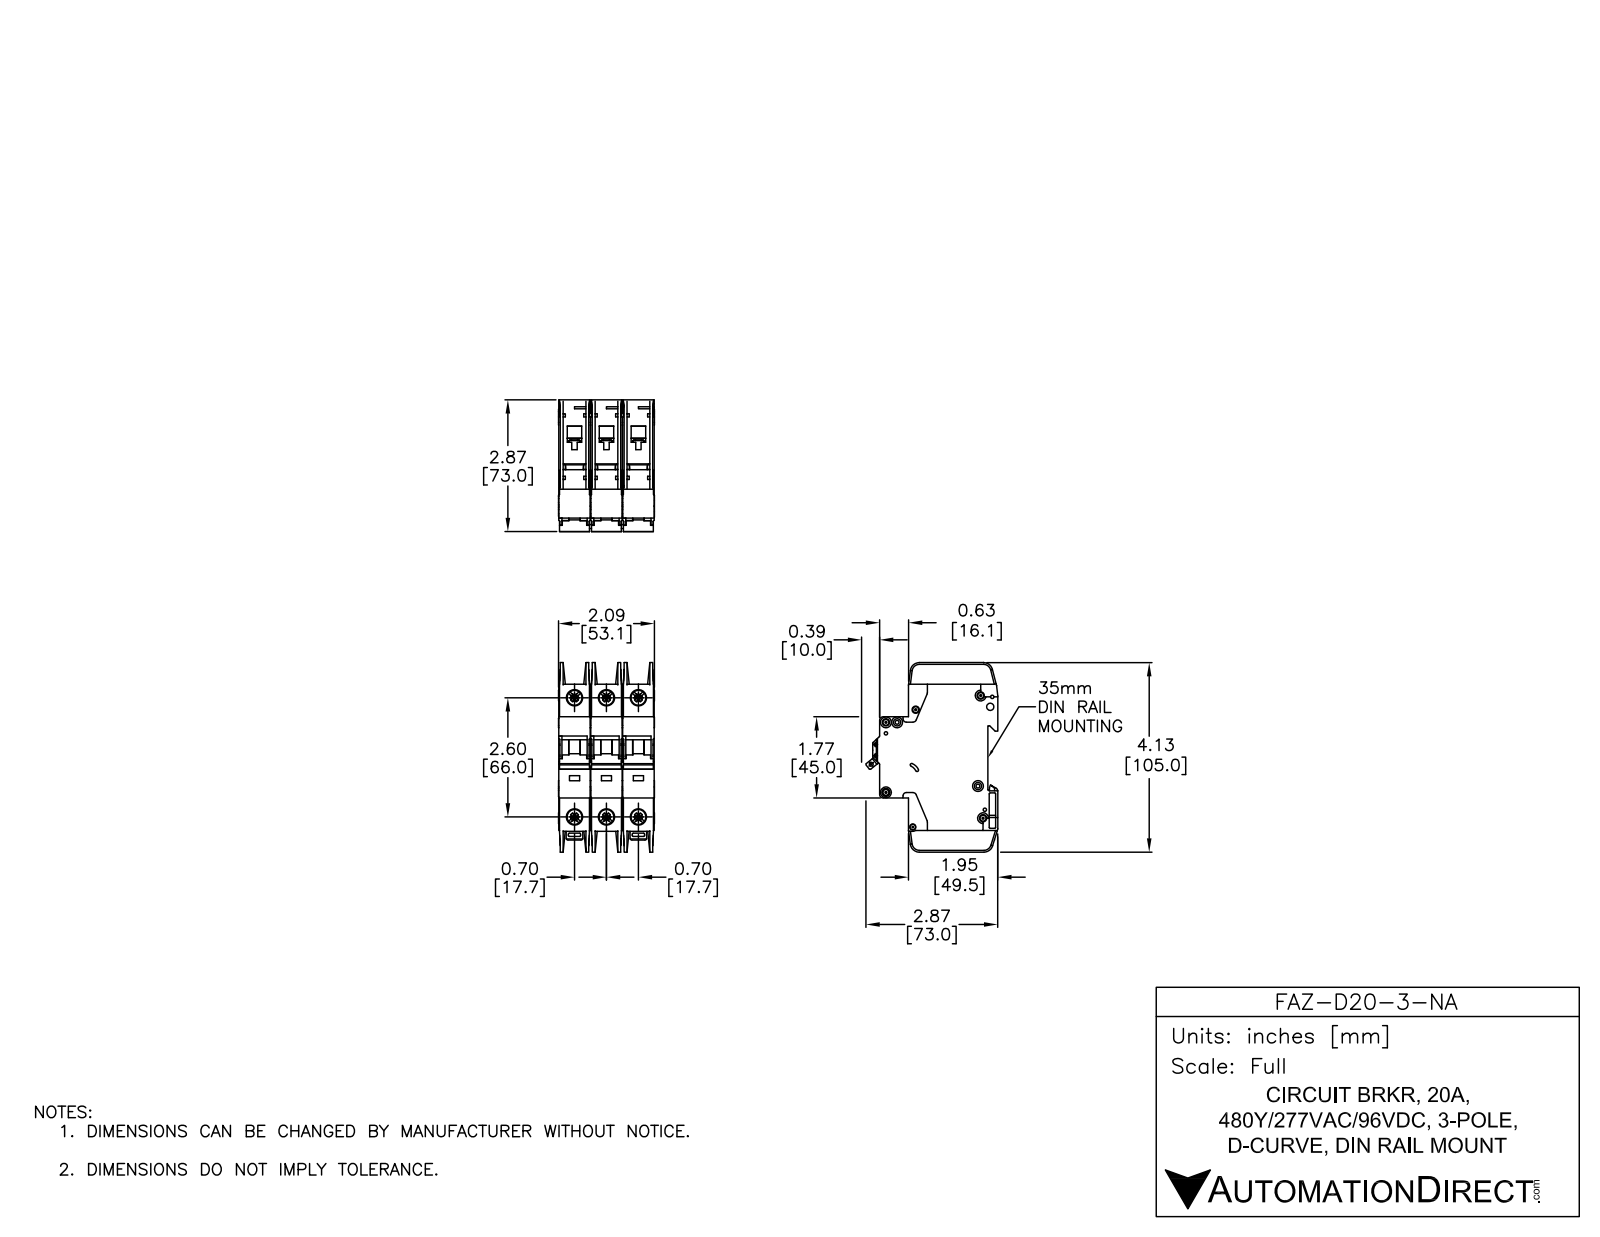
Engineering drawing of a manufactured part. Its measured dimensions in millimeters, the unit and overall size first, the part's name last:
Units: millimetres
Overall size (bounding box): 105 × 73.04 × 53.1
Round holes (diameter × count): ⌀3.6 ×7, ⌀7.15 ×6, ⌀8.2 ×6, ⌀1.09 ×2, ⌀1.5 ×2, ⌀4 ×2, ⌀1.9 ×1, ⌀2.15 ×1, ⌀2.2 ×1, ⌀2.55 ×1, ⌀3.3 ×1, ⌀3.4 ×1
Round bosses / shafts (diameter × count): ⌀6 ×7, ⌀2.5 ×3
Partial cylindrical surfaces — rounded edges, fillets, slot ends (radius × count): R0.25 ×65, R0.5 ×30, R1 ×26, R2 ×14, R1.8 ×5, R5 ×5, R4 ×4, R0.2 ×2
Main face-to-face distances: 17.7, 35.4, 17.5, 35.2, 0.7, 15.05, 2.45, 1.75, 15.75, 13.3
Hole centre spacings: 17.7, 68.33, 66, 6.2, 35.4, 74.89, 5.19, 6.1
Volume: 233 085 mm³ · Surface area: 74 219 mm²
Bodies: 9 solids, 2352 faces (1227 planar, 789 cylindrical, 336 other)
Part name (STEP PRODUCT): FAZ-D20-3-NA
STEP written by: SolidWorks 2014 (AUTOMOTIVE_DESIGN)
